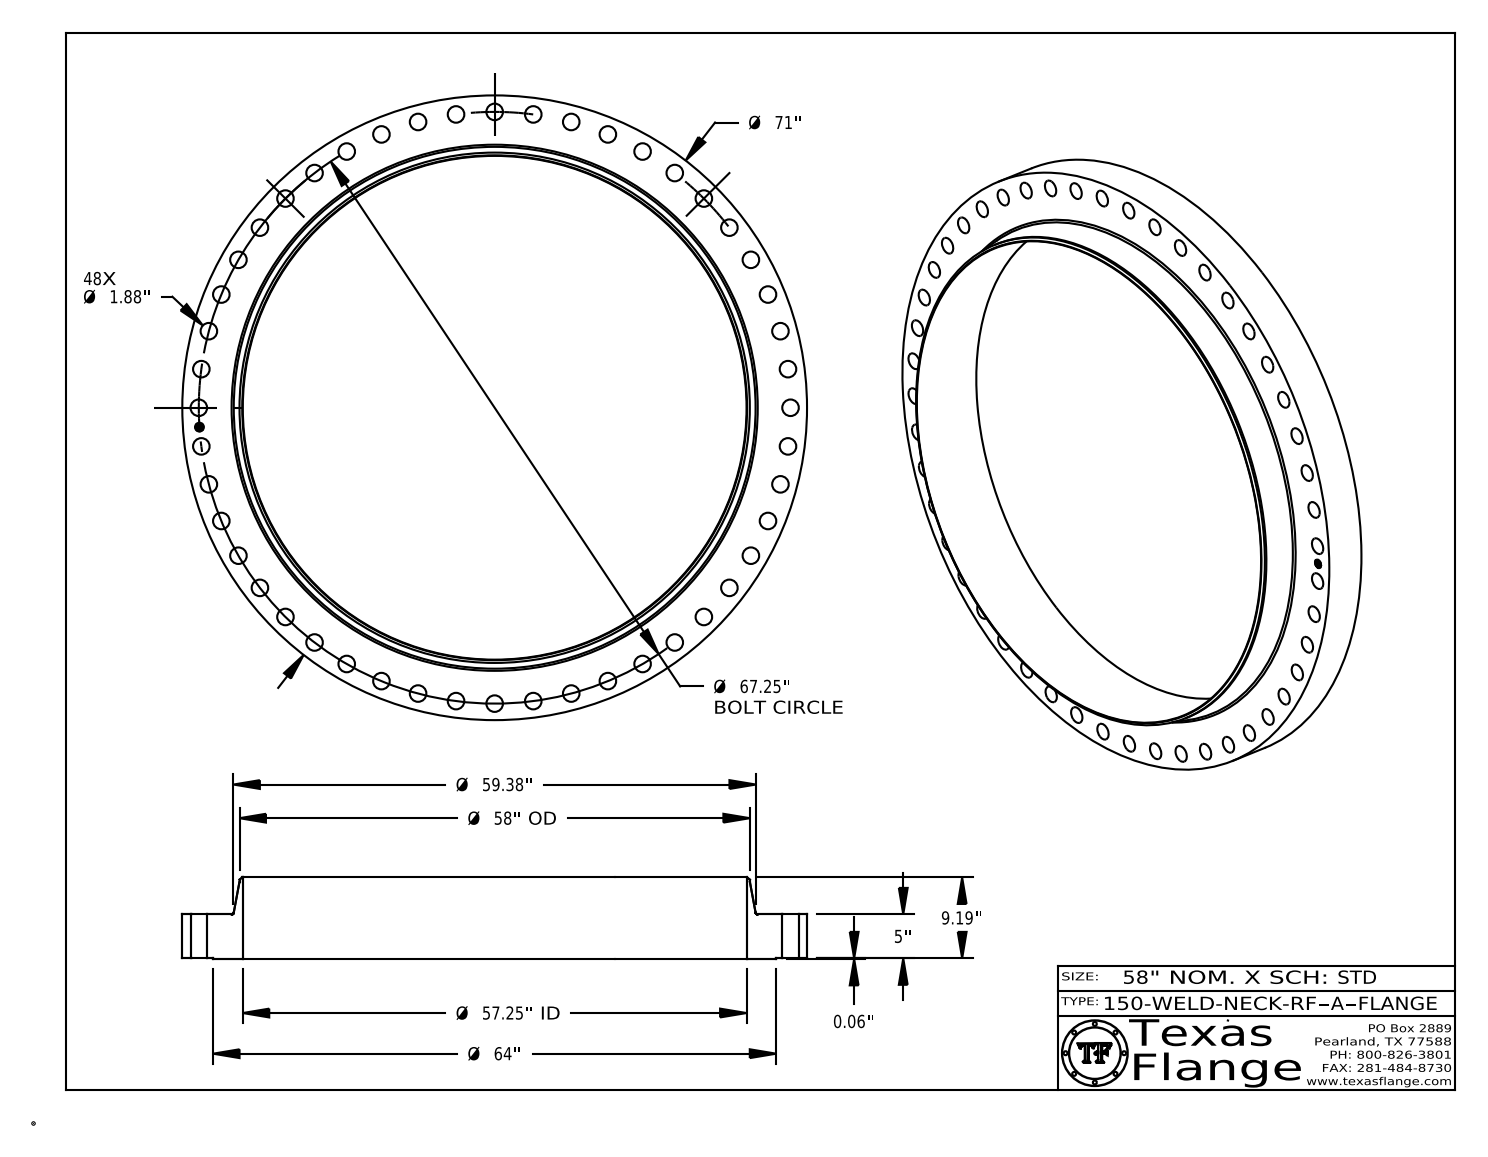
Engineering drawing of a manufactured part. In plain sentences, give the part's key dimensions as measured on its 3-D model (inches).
The part is named "150-WELD-NECK-RF, Series A". Its 3-D file was written by "CATIA V5 STEP AP214 (AUTOMOTIVE_DESIGN)". It is 1 solid with 499 faces: 369 planar, 124 cylindrical and 6 other. Overall it measures 71 by 71 by 9.253 inches. Its volume is 6 814 cubic inches and its surface area 7 328 square inches. Round holes: 48 of diameter 1.88, 1 of diameter 1, 1 of diameter 57.25. Round bosses or shafts: 8 of diameter 0.061, 1 of diameter 71, 1 of diameter 64, 1 of diameter 58, 1 of diameter 0.788. The main face-to-face distances are 5.063, 0.063, 5, 9.253, 9.19, 4.19, 0.015, 5.048, 4.985, 4.205. The hole center spacings are 33.625, 8.778, 4.398, 67.106, 17.406, 25.735, 13.12, 33.625.
